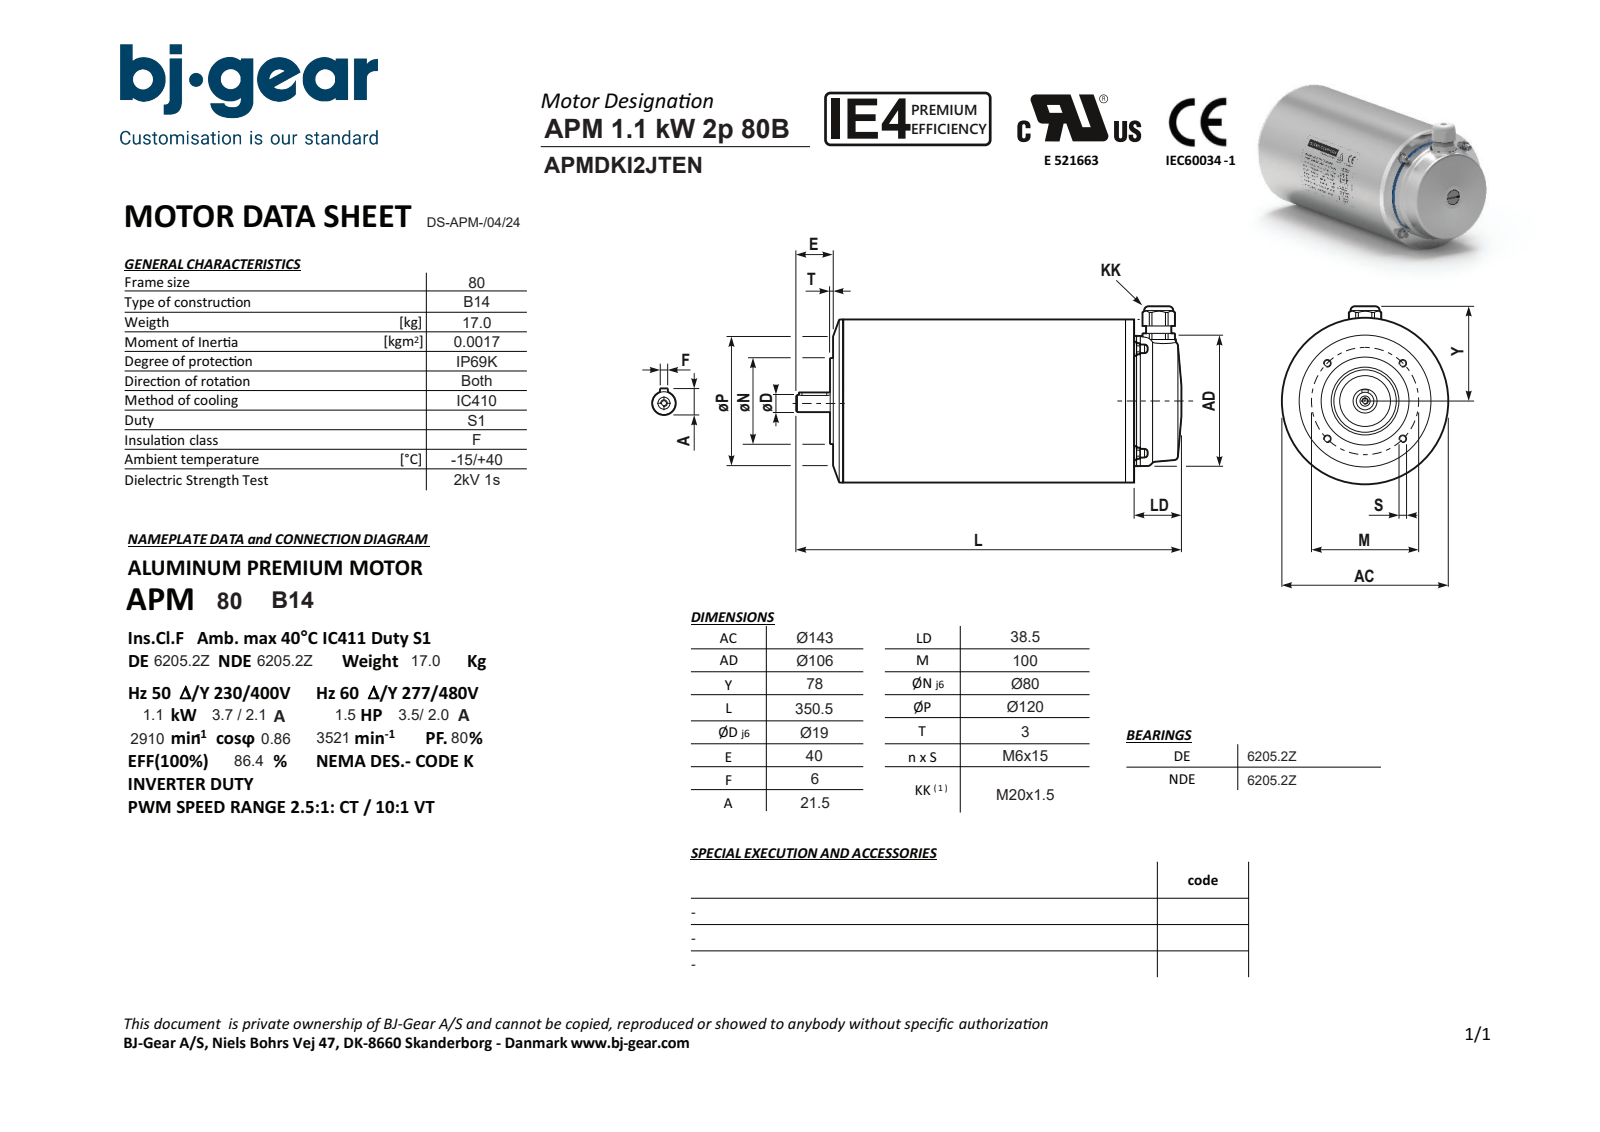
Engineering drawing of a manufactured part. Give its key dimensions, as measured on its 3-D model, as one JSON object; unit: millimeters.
{"part_name": "APMDKI2JTENN4KCR2-N---NNN", "step_written_by": "Solid Edge (AUTOMOTIVE_DESIGN)", "units": "millimeters", "bodies": {"solids": 1, "faces": 156, "planar": 75, "cylindrical": 50, "other": 31}, "overall_size": [350.5, 148.3, 142.6], "volume_mm3": 4636000, "surface_area_mm2": 172344, "round_holes": [[4.92, 5], [6.4, 1], [16, 1], [28, 1], [65, 1]], "round_bosses_or_shafts": [[11.5, 4], [7, 4], [142.6, 1], [142.6, 1], [106, 1], [80, 1], [25, 1], [23.7, 1]], "partial_cylinders_radius": [[3, 2], [13.2, 1]], "face_to_face_distances": [272, 6, 266, 9, 3, 275, 24, 310.5, 38.5, 304.5], "hole_center_spacings": [50.01, 70.72, 100.01]}
